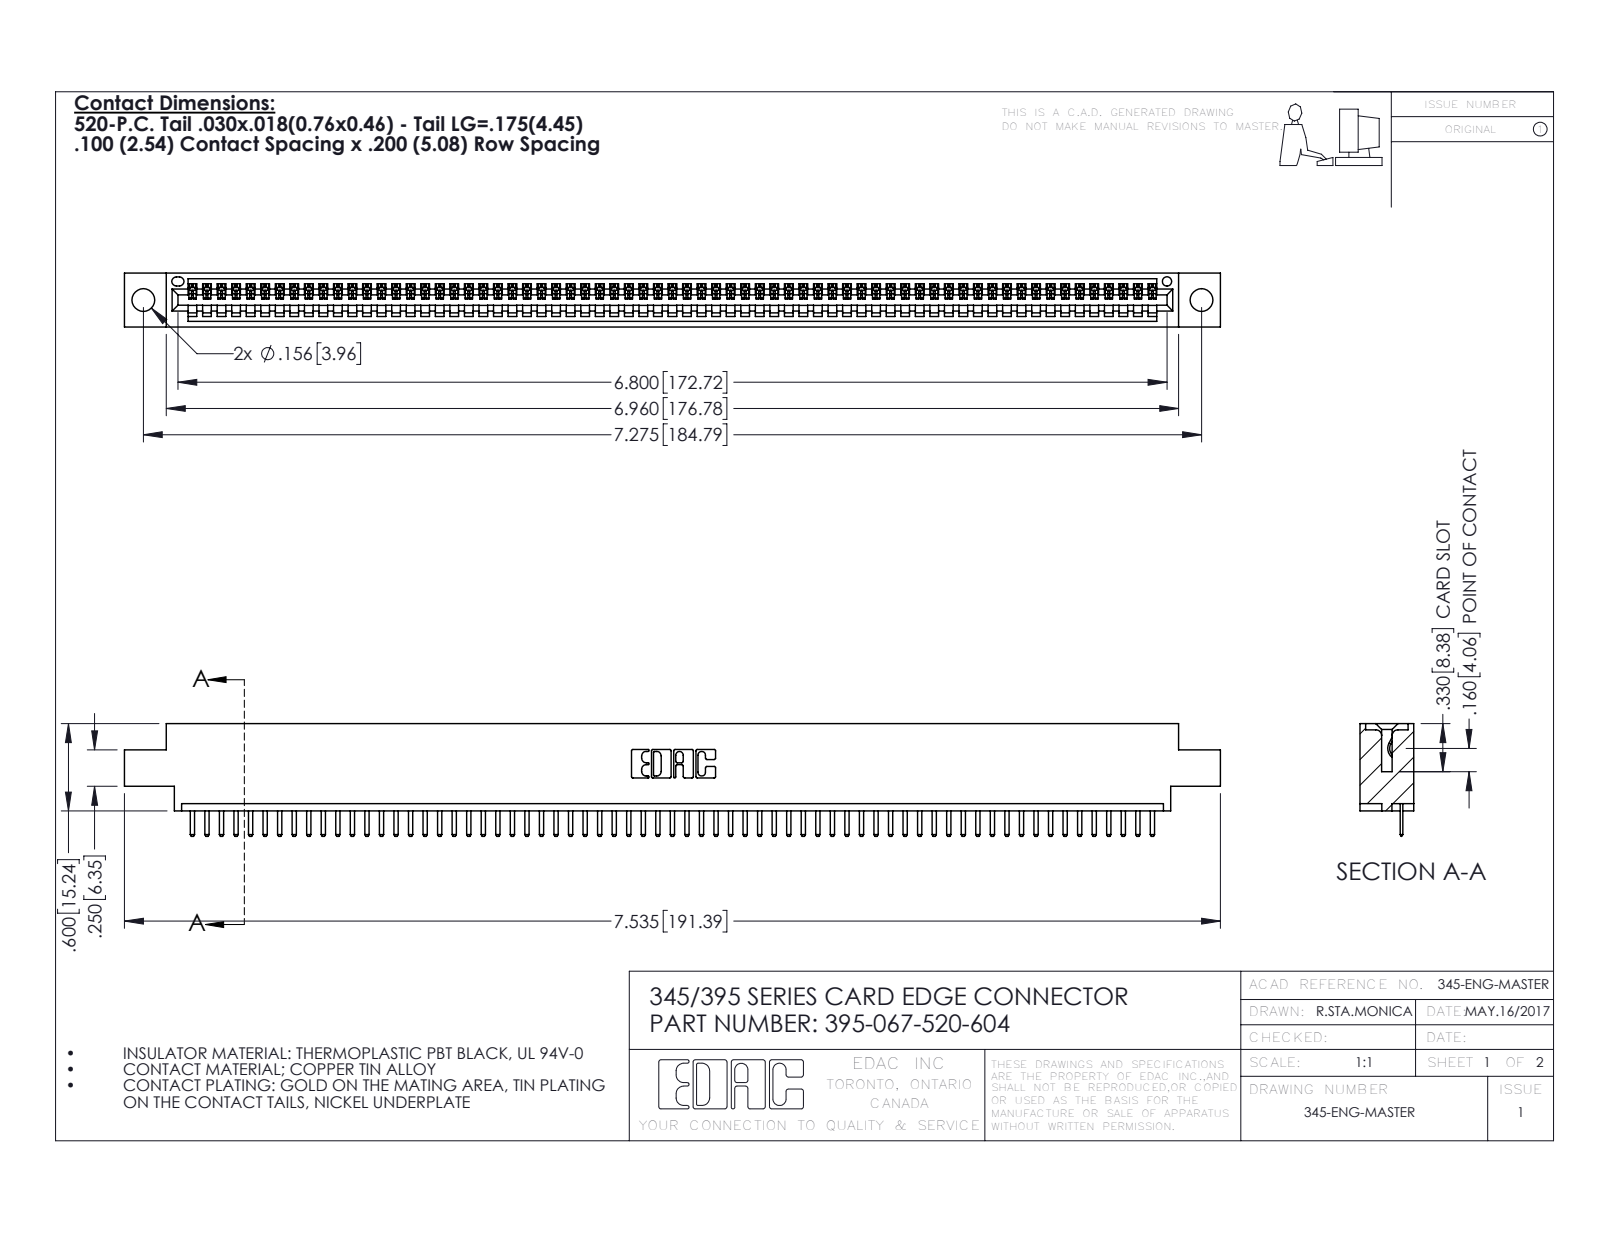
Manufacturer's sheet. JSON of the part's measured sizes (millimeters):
{"part_name": "395-067-520-604; 345-292-001_345-293-120; 345 Part_0.170 Offset - 0.156 Dia-TH", "step_written_by": "SolidWorks 2016 (CONFIG_CONTROL_DESIGN)", "units": "millimeters", "bodies": {"solids": 68, "faces": 4284, "planar": 2898, "cylindrical": 1386, "other": 0}, "overall_size": [191.4, 19.7, 9.4], "volume_mm3": 17990, "surface_area_mm2": 23550, "round_holes": [[4, 2], [1.6, 1]], "partial_cylinders_radius": [[0.3, 136], [0.2, 134], [0.3, 22], [0.2, 6], [0.8, 6], [0.7, 3], [0.8, 2], [1, 2]], "face_to_face_distances": [7.6, 1.8, 9.4, 5.1, 2.5, 6.9, 0.6, 5.7, 1.8, 4.4], "hole_center_spacings": [6.9, 178.8, 184.8]}
